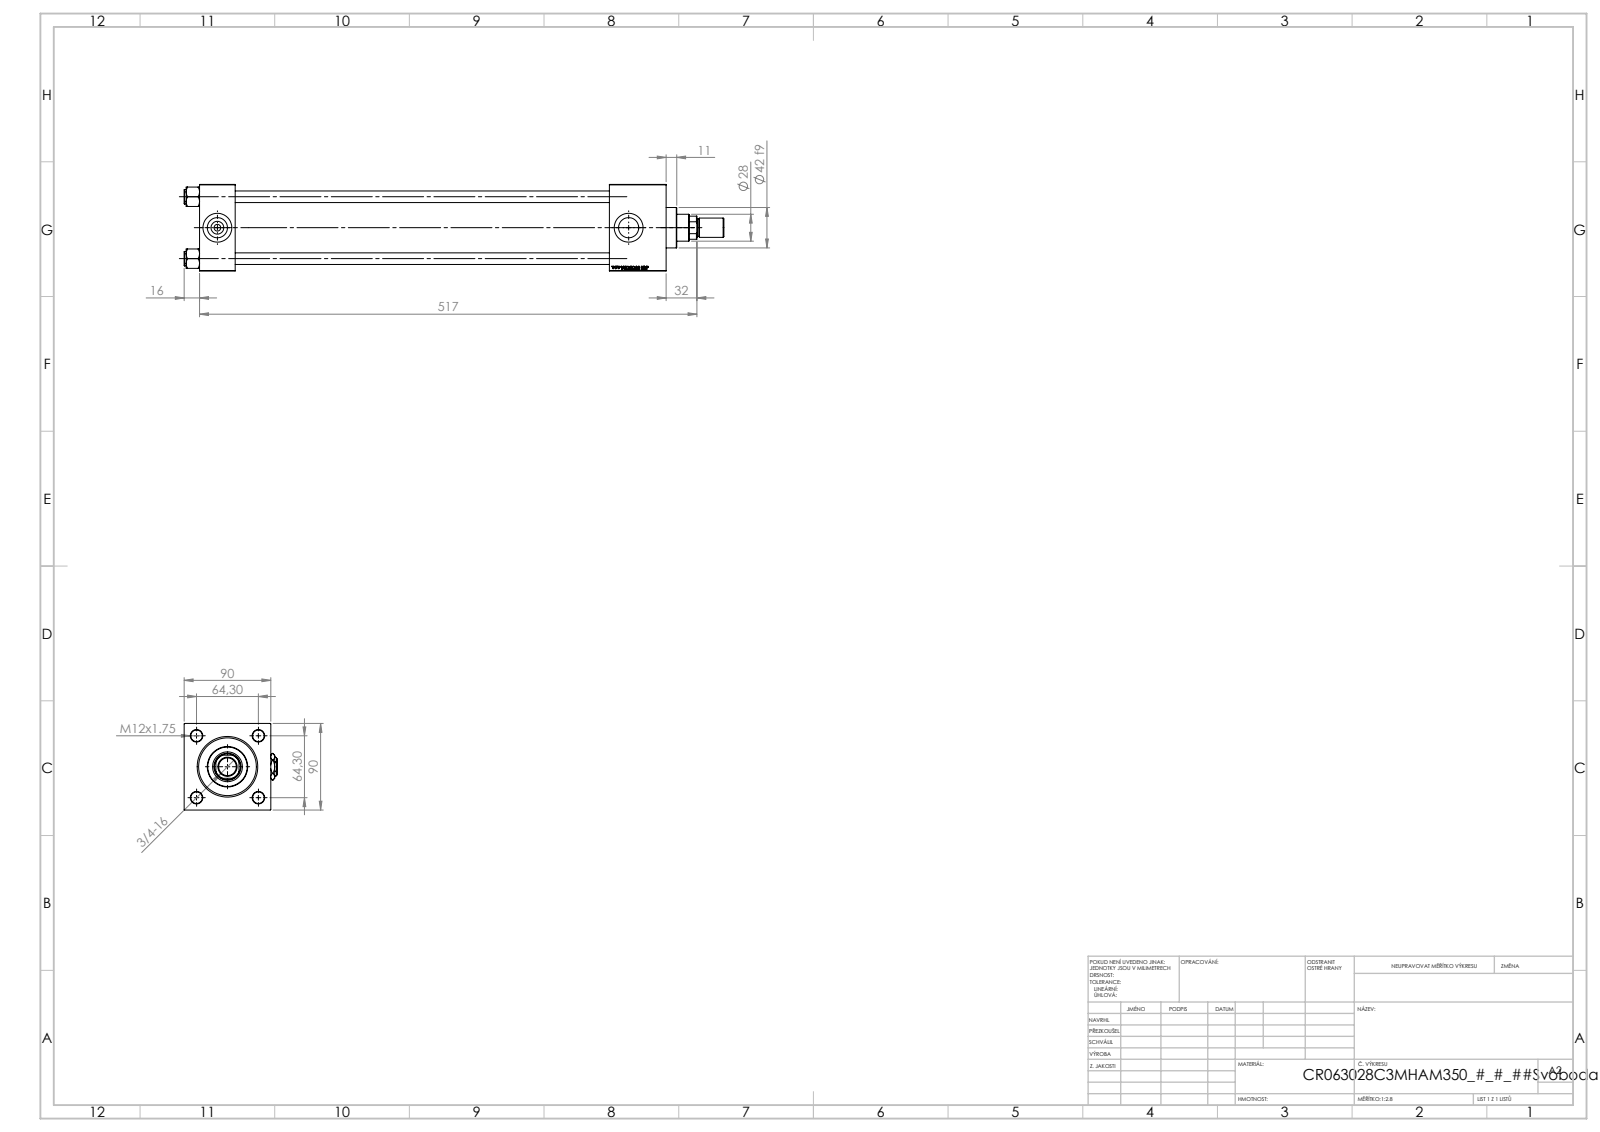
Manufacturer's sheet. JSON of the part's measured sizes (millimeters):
{"part_name": "ROD_END_AH; NUT_M5_C; V215CR_C_Body; V215CR_VCP_C (+3 more)", "step_written_by": "SolidWorks 2019 (CONFIG_CONTROL_DESIGN)", "units": "millimeters", "bodies": {"solids": 14, "faces": 1264, "planar": 578, "cylindrical": 102, "other": 584}, "overall_size": [561, 97, 90], "volume_mm3": 1507000, "surface_area_mm2": 401988, "round_holes": [[12, 4], [7, 2], [20.96, 2], [30, 2], [18.5, 1], [28, 1], [31, 1], [50, 1], [60, 1], [63, 1]], "round_bosses_or_shafts": [[15, 4], [69, 1], [42, 1], [20, 1], [18, 1]], "partial_cylinders_radius": [[13.5, 1]], "face_to_face_distances": [90, 37, 448, 485, 59, 426, 389, 456.3, 419.3, 30.3], "hole_center_spacings": [45.47, 64.3, 90.93, 427.5]}
